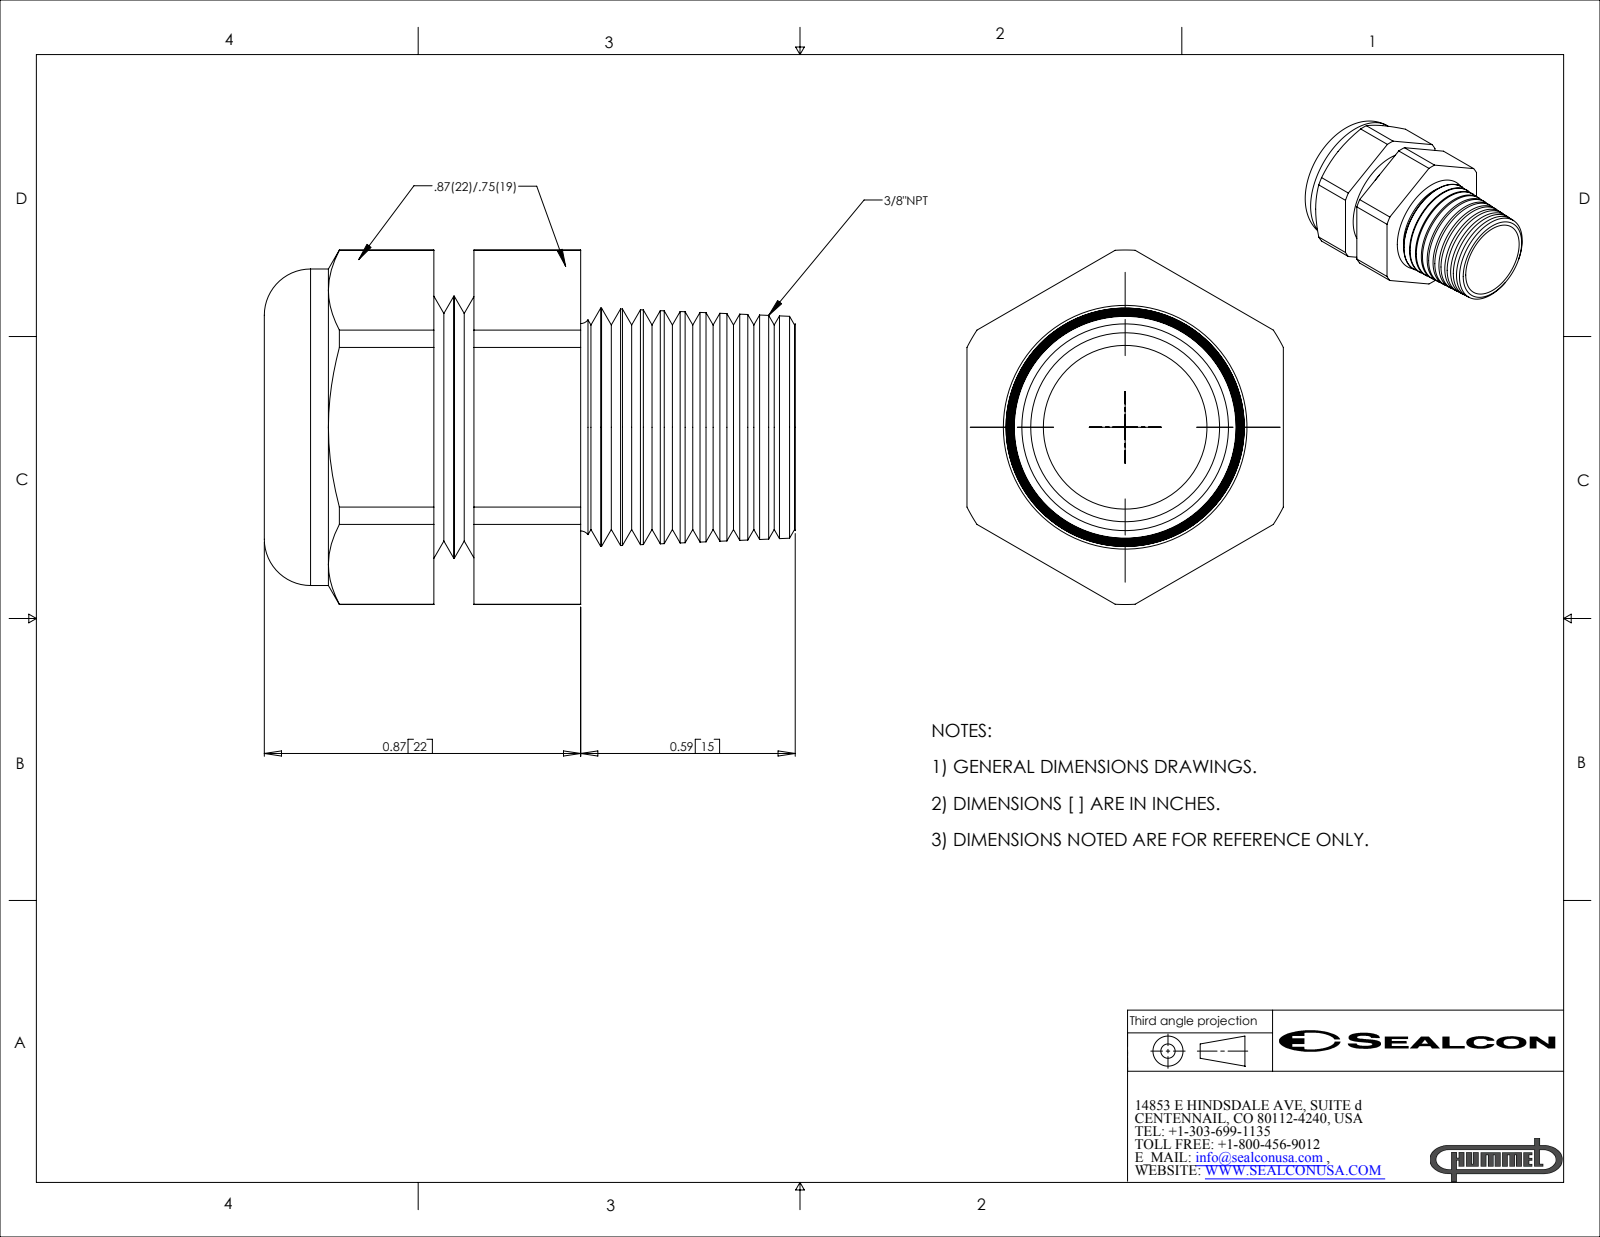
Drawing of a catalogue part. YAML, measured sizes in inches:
part_name: "CD09NA-GY"
step_written_by: "SolidWorks 2007 (CONFIG_CONTROL_DESIGN)"
units: inches
bodies: {solids: 2, faces: 134, planar: 20, cylindrical: 26, other: 88}
overall_size: [1.46, 0.974, 0.87]
volume: 0.424
surface_area: 8.789
round_holes:
  - {diameter: 0.45, count: 1}
  - {diameter: 0.561, count: 1}
  - {diameter: 0.721, count: 1}
round_bosses_or_shafts:
  - {diameter: 0.87, count: 1}
partial_cylinders:
  - {radius: 0.487, count: 1}
face_to_face_distances: [0.87, 0.294, 0.11, 0.404, 0.29, 0.4, 0.694, 0.156, 0.446, 0.556]
